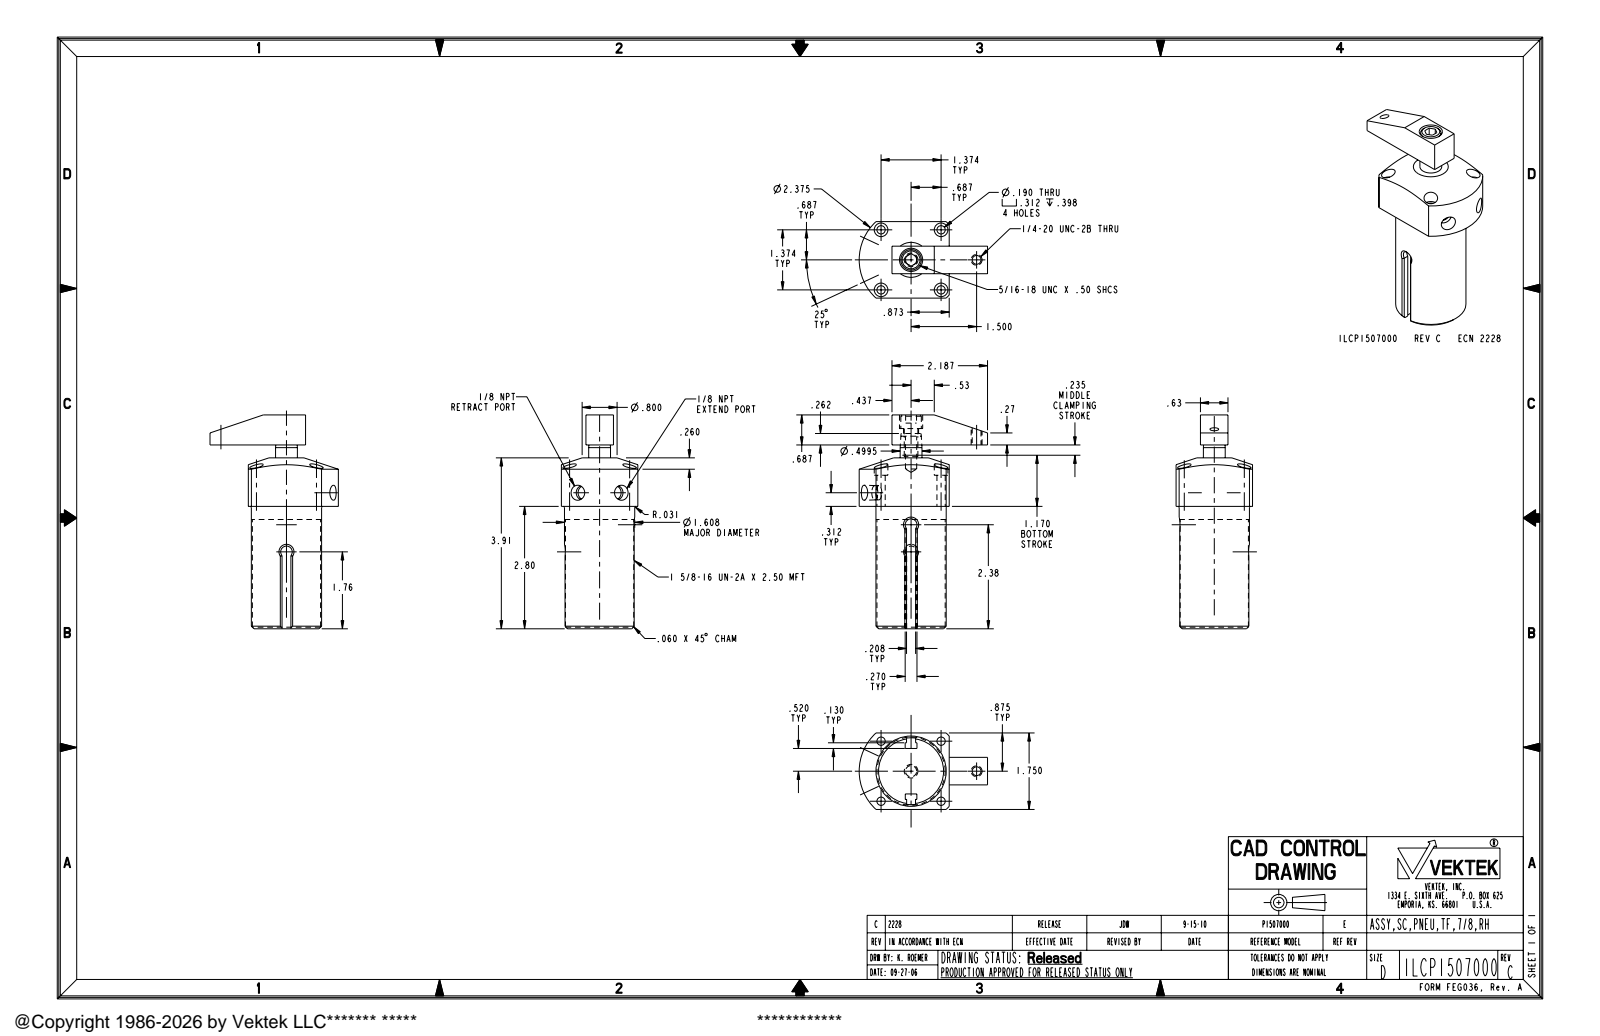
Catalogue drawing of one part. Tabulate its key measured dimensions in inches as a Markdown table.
| quantity | value |
| --- | --- |
| part name | ILCP1507600; ILC91500903; ILCP1507600_ASM |
| STEP written by | PRO/ENGINEER BY PARAMETRIC TECHNOLOGY CORPORATION, 2007460 (AUTOMOTIVE_DESIGN_CC2) |
| units | inches |
| bodies | 2 solids, 123 faces (52 planar, 47 cylindrical, 24 other) |
| overall size | 4.892 × 2.938 × 1.75 |
| volume | 9.334 in³ |
| surface area | 55.05 in² |
| round holes (diameter × count) | 0.19 × 4, 0.312 × 4, 0.328 × 2, 0.201 × 1, 0.257 × 1, 0.344 × 1, 0.531 × 1 |
| round bosses / shafts (diameter × count) | 1.608 × 1, 1.562 × 1, 0.5 × 1, 0.469 × 1, 0.312 × 1, 0.25 × 1 |
| partial cylindrical surfaces (radius × count) | 0.132 × 1, 0.135 × 1, 1.187 × 1 |
| main face-to-face distances | 1.75, 0.562, 1.192, 0.558, 0.63, 1.188, 0.355, 1.395, 4.205, 1.405 |
| hole center spacings | 0.972, 1.374, 1.065, 1.943, 2.293, 1.5 |
